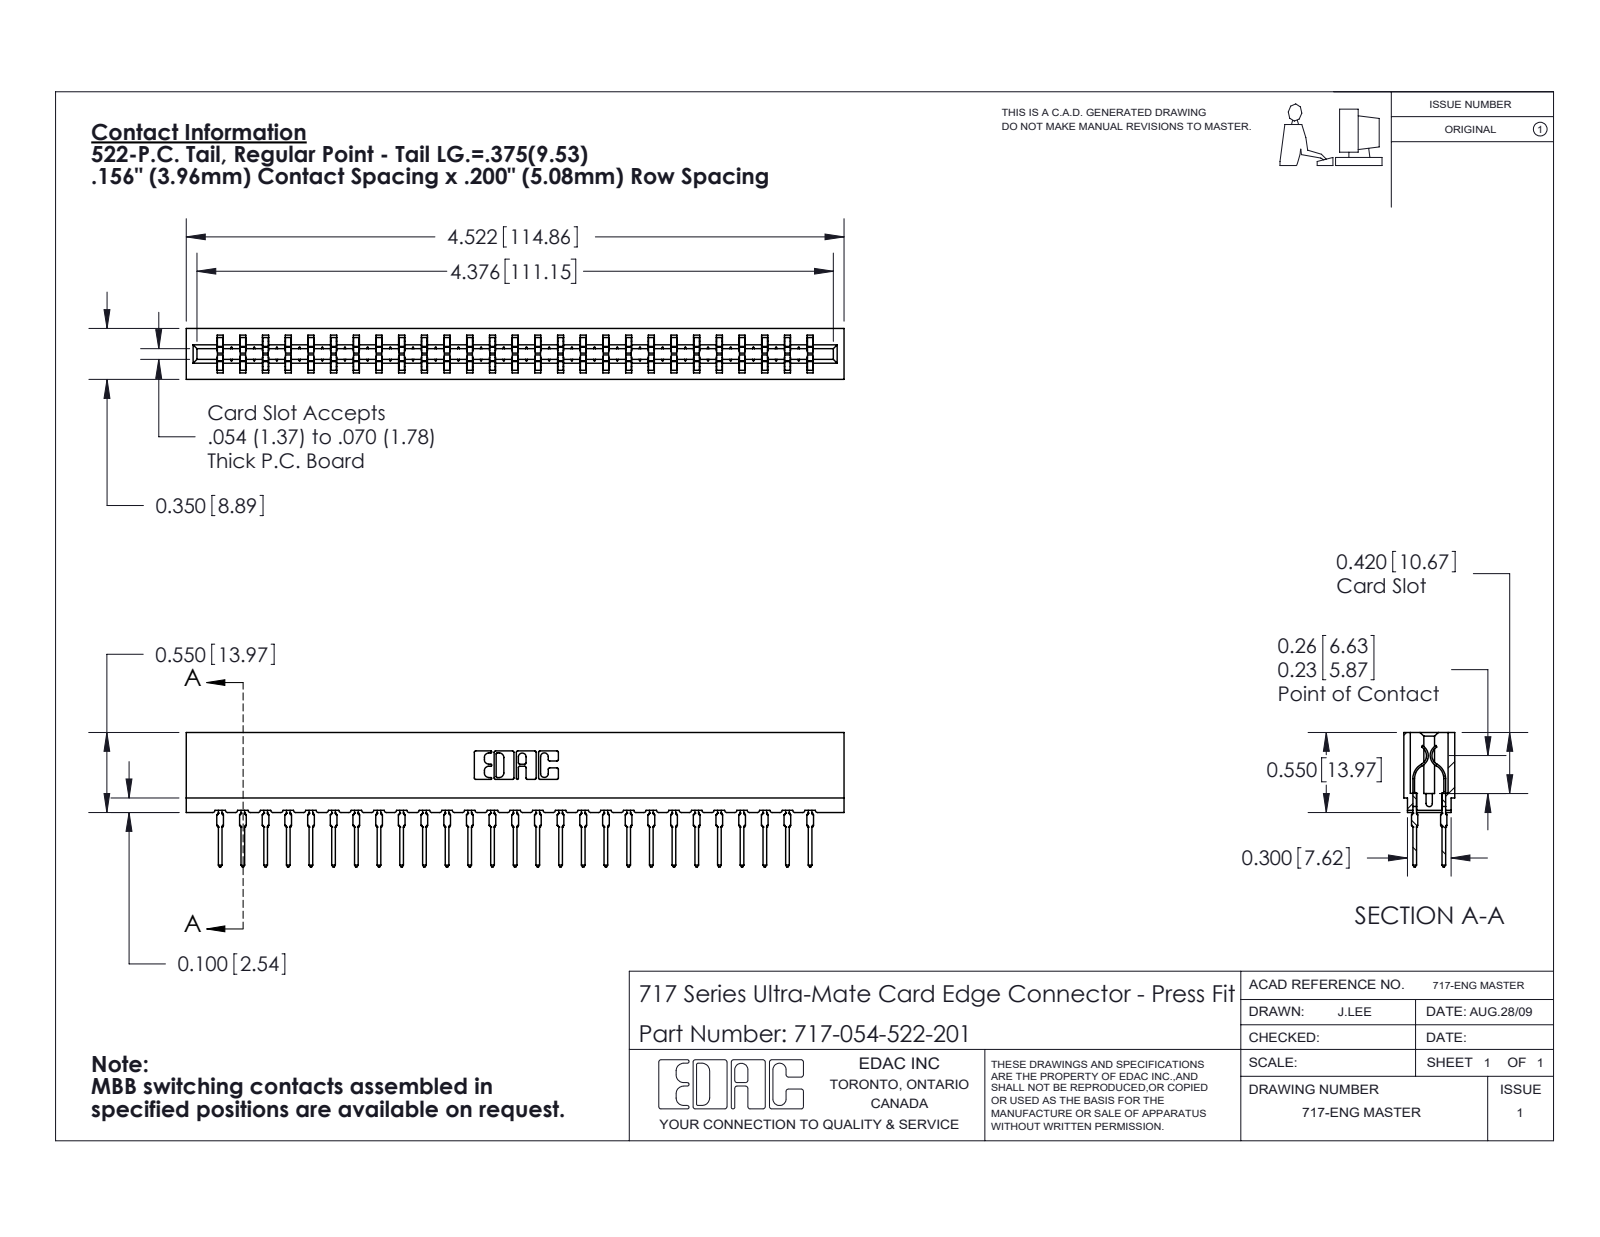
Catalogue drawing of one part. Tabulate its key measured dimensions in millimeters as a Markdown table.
| quantity | value |
| --- | --- |
| part name | 717 Part_Insulator Option - 06; 717-054-522-201; 745-292-001_522 |
| STEP written by | SolidWorks 2020 (CONFIG_CONTROL_DESIGN) |
| units | millimeters |
| bodies | 55 solids, 4954 faces (2565 planar, 985 cylindrical, 1404 other) |
| overall size | 114.9 × 23.5 × 8.9 |
| volume | 10 100 mm³ |
| surface area | 15 420 mm² |
| partial cylindrical surfaces (radius × count) | 0.5 × 108, 0.4 × 54, 0.3 × 22, 0.1 × 8, 0.3 × 8, 0.2 × 6, 0.8 × 6, 0.7 × 3 |
| main face-to-face distances | 5.4, 3.5, 8.9, 1.6, 7.3, 1.9, 3.8, 4, 1.9, 1.1 |
